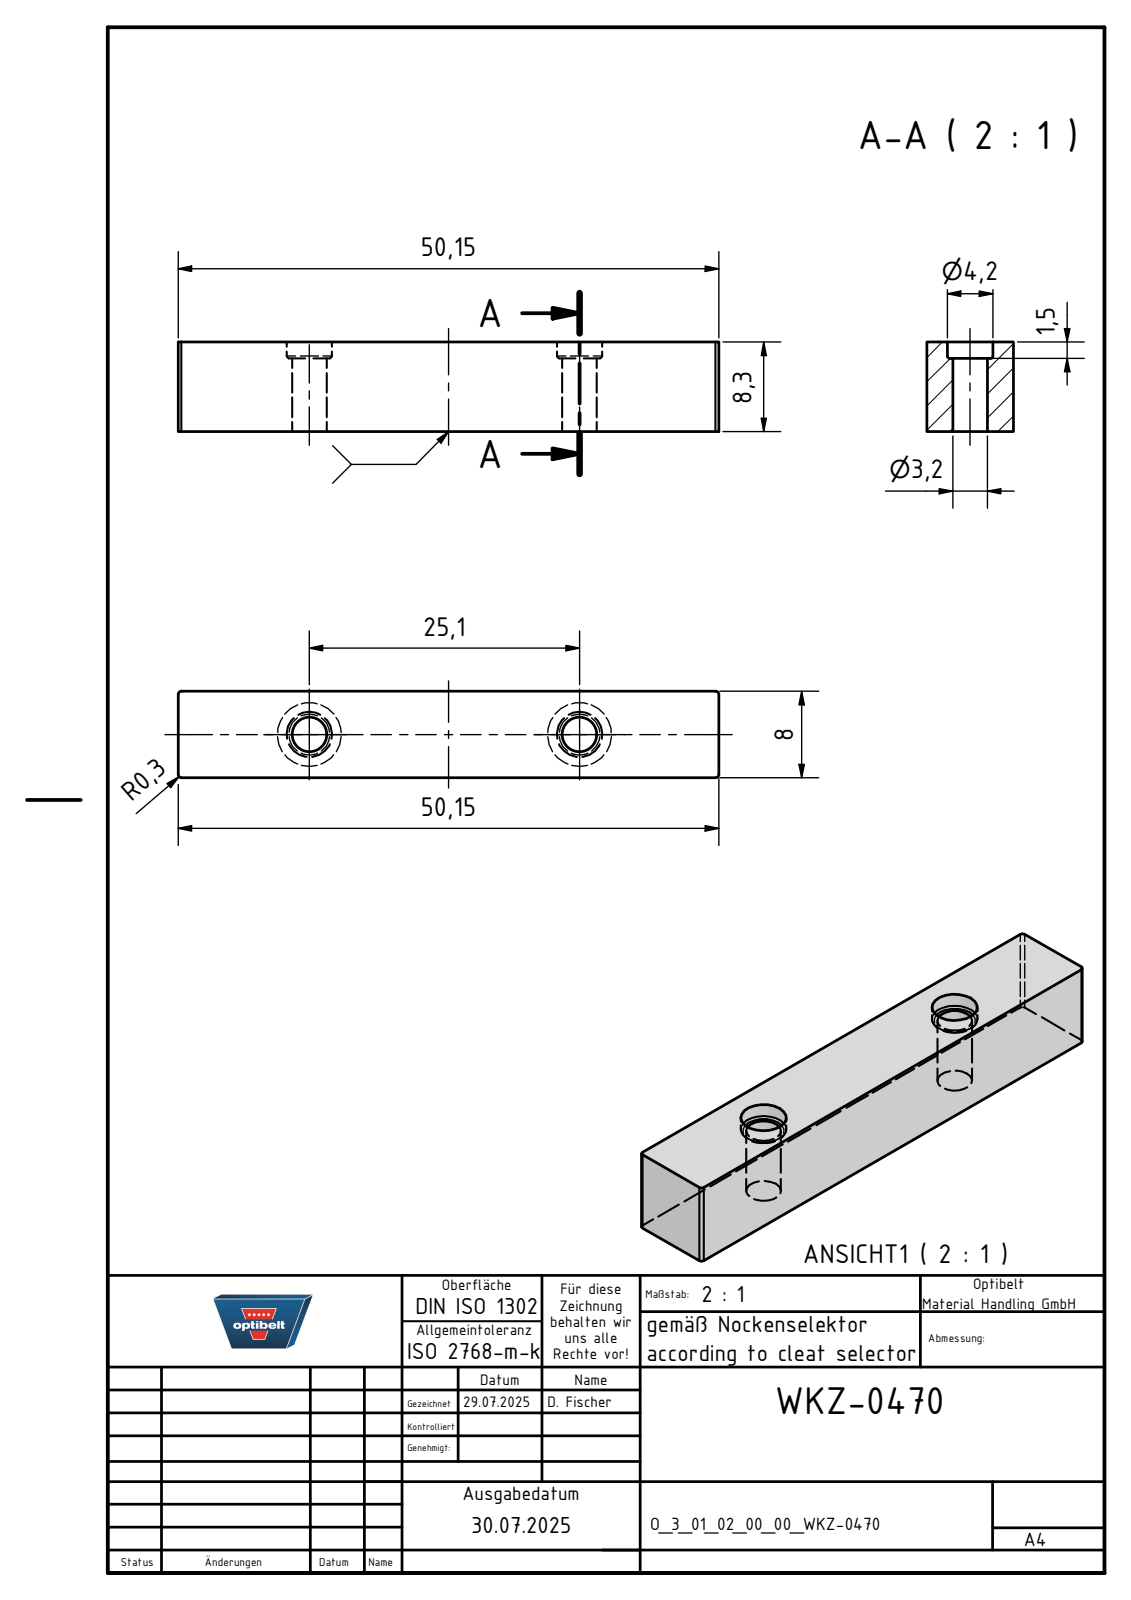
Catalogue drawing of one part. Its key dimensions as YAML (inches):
part_name: "O_3_01_02_00_00_WKZ-0470"
step_written_by: "Autodesk Inventor 2025 (AUTOMOTIVE_DESIGN)"
units: inches
bodies: {solids: 1, faces: 21, planar: 11, cylindrical: 8, other: 2}
overall_size: [1.974, 0.328, 0.316]
volume: 0.195
surface_area: 2.964
round_holes:
  - {diameter: 0.126, count: 2}
  - {diameter: 0.166, count: 2}
partial_cylinders:
  - {radius: 0.012, count: 4}
face_to_face_distances: [0.316, 0.328, 1.974, 0.269, 0.059]
hole_center_spacings: [0.987]
